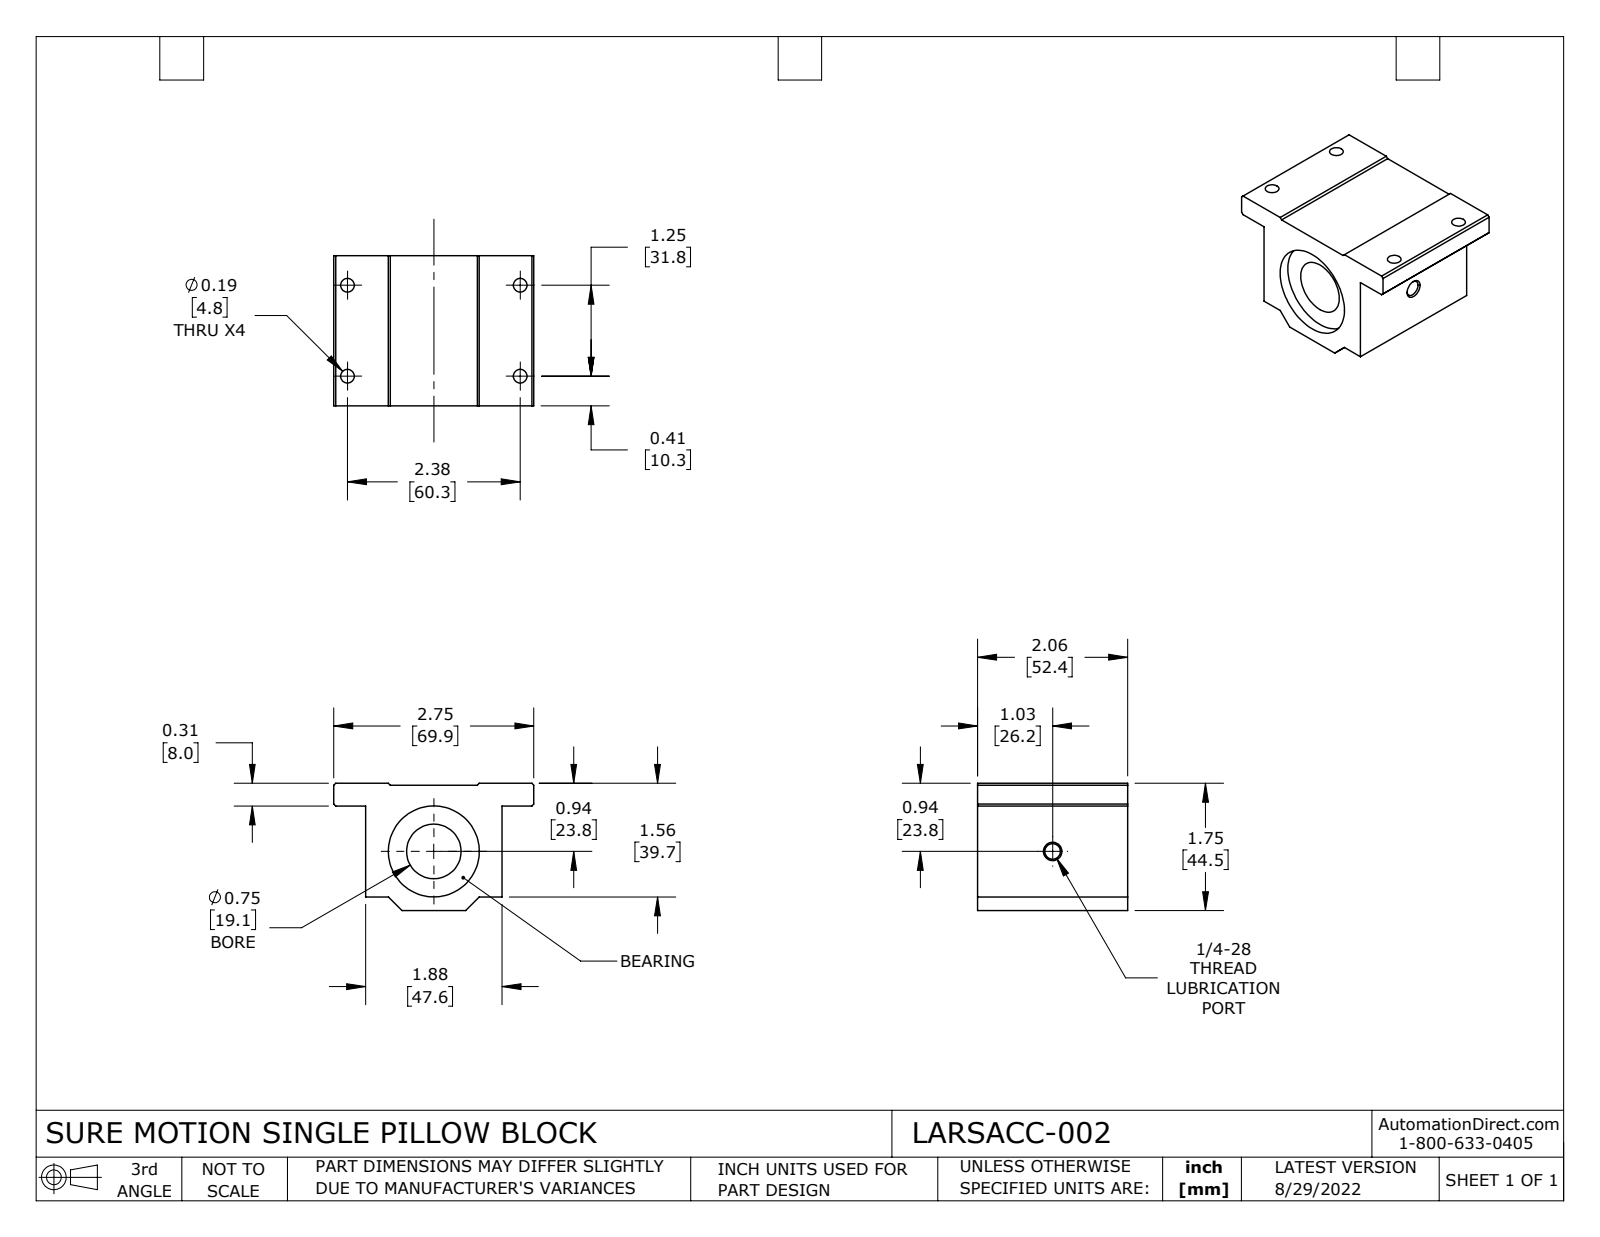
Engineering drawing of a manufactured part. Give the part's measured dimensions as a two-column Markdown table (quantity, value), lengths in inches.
| quantity | value |
| --- | --- |
| part name | LARSACC-002 |
| STEP written by | SolidWorks 2021 (CONFIG_CONTROL_DESIGN) |
| units | inches |
| bodies | 1 solid, 44 faces (24 planar, 18 cylindrical, 2 other) |
| overall size | 2.75 × 2.063 × 1.75 |
| volume | 5.755 in³ |
| surface area | 29.94 in² |
| round holes (diameter × count) | 0.188 × 4, 0.213 × 1, 0.75 × 1, 1.25 × 1 |
| main face-to-face distances | 1.876, 0.028, 2.063, 1.722, 1.75, 1.437, 0.285, 0.313, 0.15, 1.913 |
| hole center spacings | 1.25, 2.376, 2.684 |
